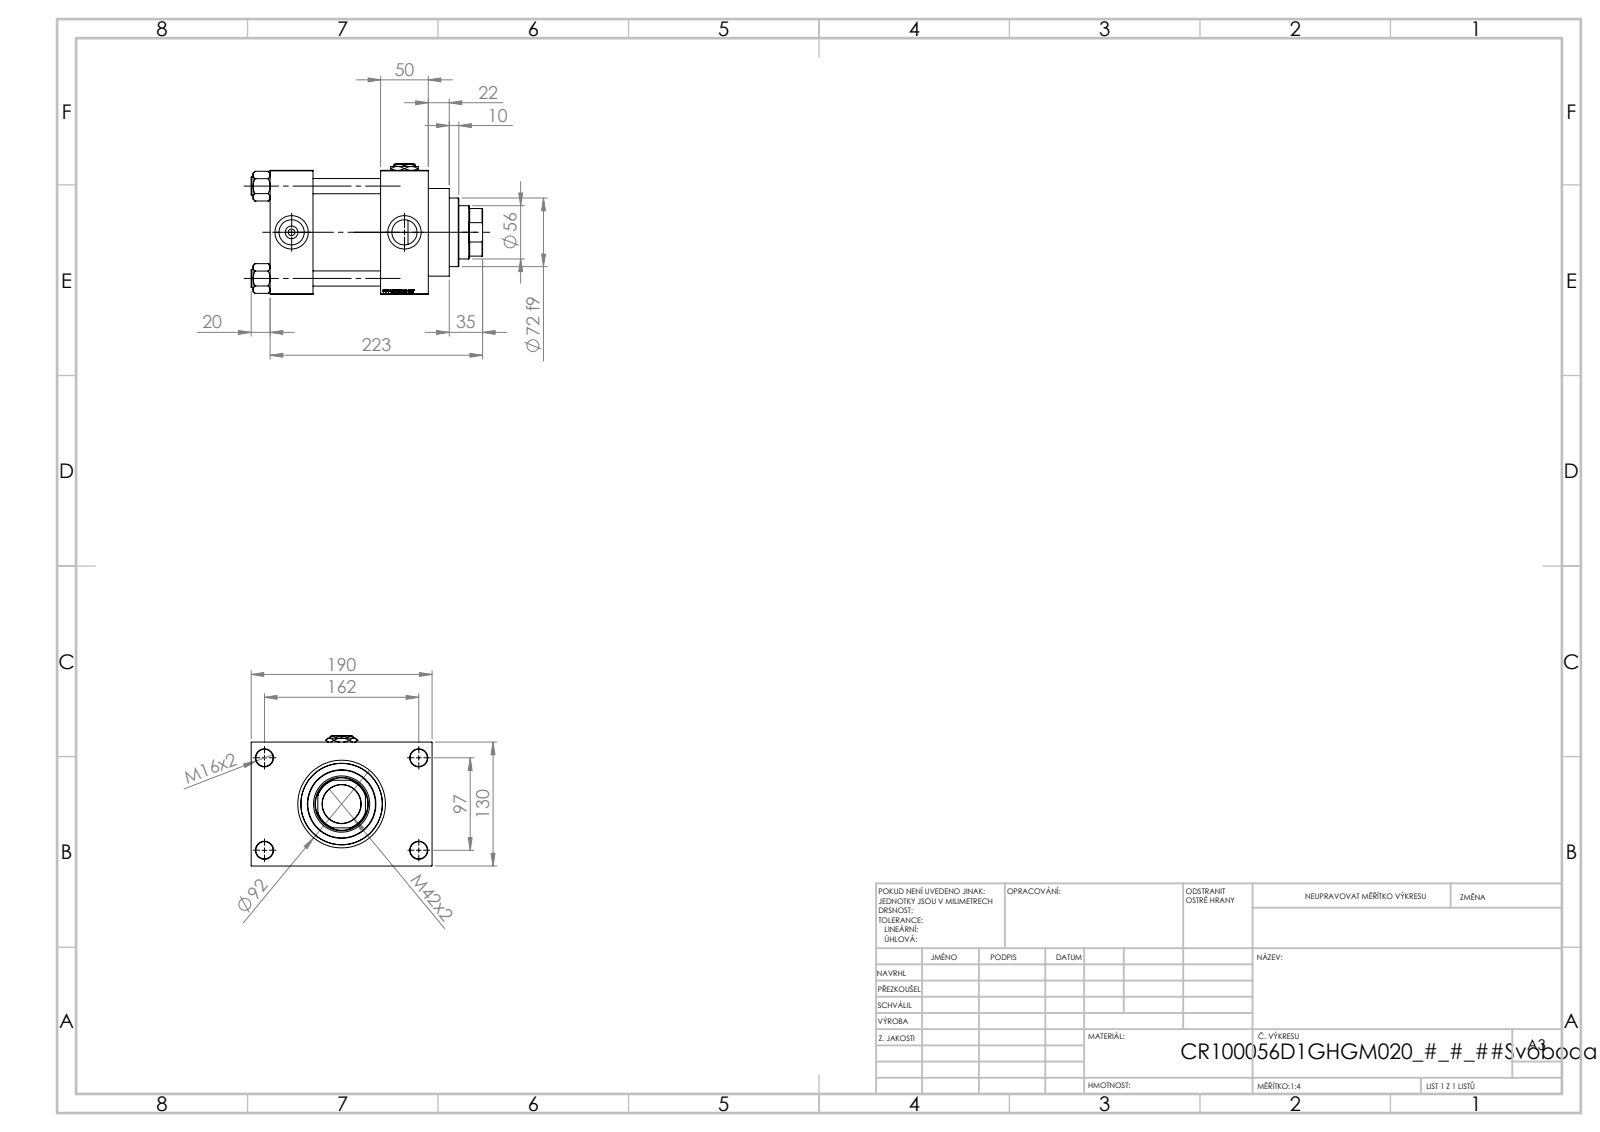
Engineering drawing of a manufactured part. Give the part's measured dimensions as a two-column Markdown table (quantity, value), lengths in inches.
| quantity | value |
| --- | --- |
| part name | V215_VC_A; V215CR_D_Body; V215CR_D_TYCINKA; NUT_M5_D (+2 more) |
| STEP written by | SolidWorks 2019 (CONFIG_CONTROL_DESIGN) |
| units | inches |
| bodies | 12 solids, 1199 faces (569 planar, 92 cylindrical, 538 other) |
| overall size | 9.567 × 7.48 × 5.394 |
| volume | 159.8 in³ |
| surface area | 566.3 in² |
| round holes (diameter × count) | 0.63 × 4, 0.709 × 4, 1.041 × 3, 1.378 × 3, 0.276 × 2, 1.594 × 1, 2.205 × 1, 2.323 × 1, 2.992 × 1, 3.366 × 1, 3.937 × 1 |
| round bosses / shafts (diameter × count) | 0.748 × 4, 4.173 × 1, 3.622 × 1, 2.835 × 1 |
| partial cylindrical surfaces (radius × count) | 1.063 × 1 |
| main face-to-face distances | 5.118, 4.567, 1.969, 1.772, 2.795, 6.535, 4.764, 1.181, 6.299, 0.787 |
| hole center spacings | 1.281, 2.698, 3.717, 3.815, 4.026, 5.096, 6.367, 3.819 |
